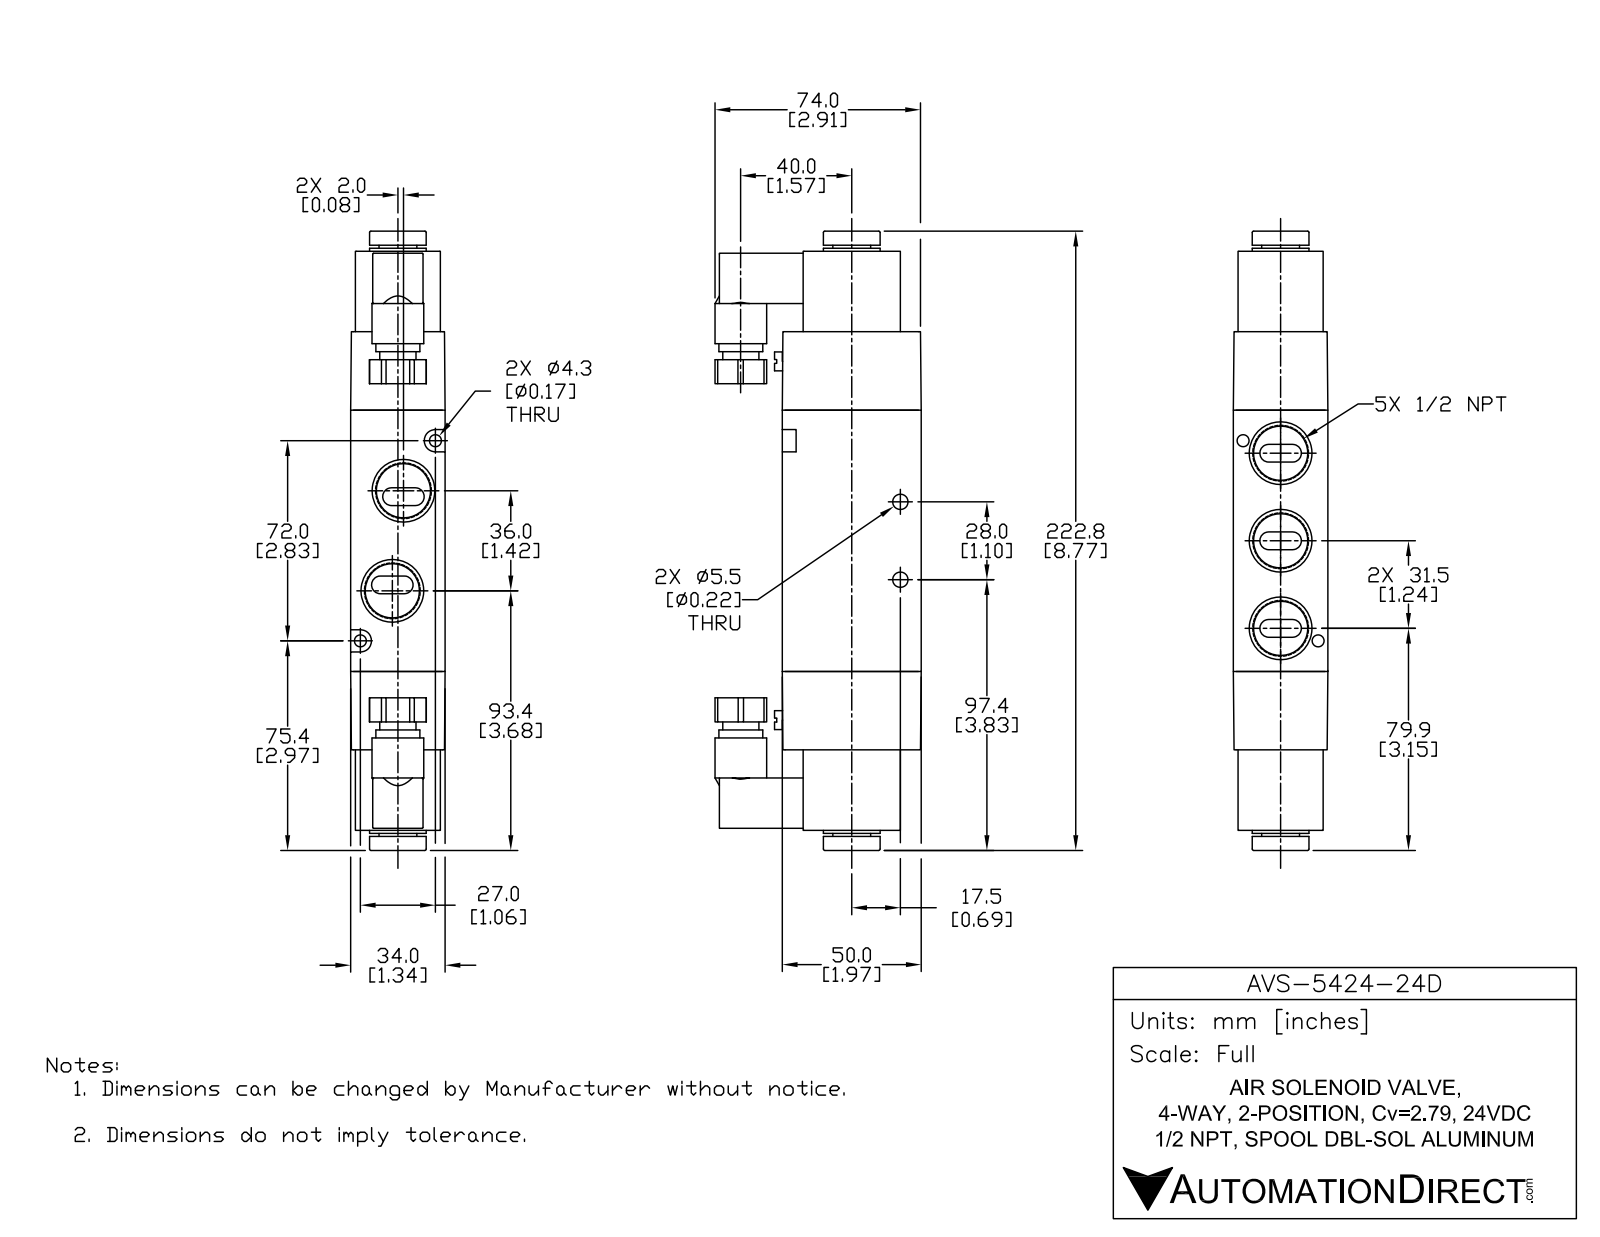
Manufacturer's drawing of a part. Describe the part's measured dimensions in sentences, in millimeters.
The part is named "AVS-5424-24D". Its 3-D file was written by "SolidWorks 2015 (CONFIG_CONTROL_DESIGN)". It is 5 solids with 248 faces: 111 planar, 103 cylindrical and 34 other. Overall it measures 222.8 by 74.2 by 34 millimeters. Its volume is 320 577 cubic millimeters and its surface area 60 995 square millimeters. Round holes: 5 of diameter 17.86, 2 of diameter 4.3, 2 of diameter 5.5, 1 of diameter 9.3. Round bosses or shafts: 2 of diameter 6.7, 1 of diameter 20.8, 1 of diameter 20.4, 1 of diameter 18.6, 1 of diameter 15.8, 1 of diameter 13.6, 1 of diameter 13. Partial cylindrical surfaces (rounded edges, fillets, slot ends): 18 of radius 1.5, 10 of radius 1, 10 of radius 3.2, 2 of radius 4. The main face-to-face distances are 34, 94, 35.6, 50, 28.2, 31.96, 51.6, 7.95, 26.05, 18.1. The hole center spacings are 13.65, 14.23, 18.11, 21.36, 31.5, 38.45, 49.54, 56.18.
